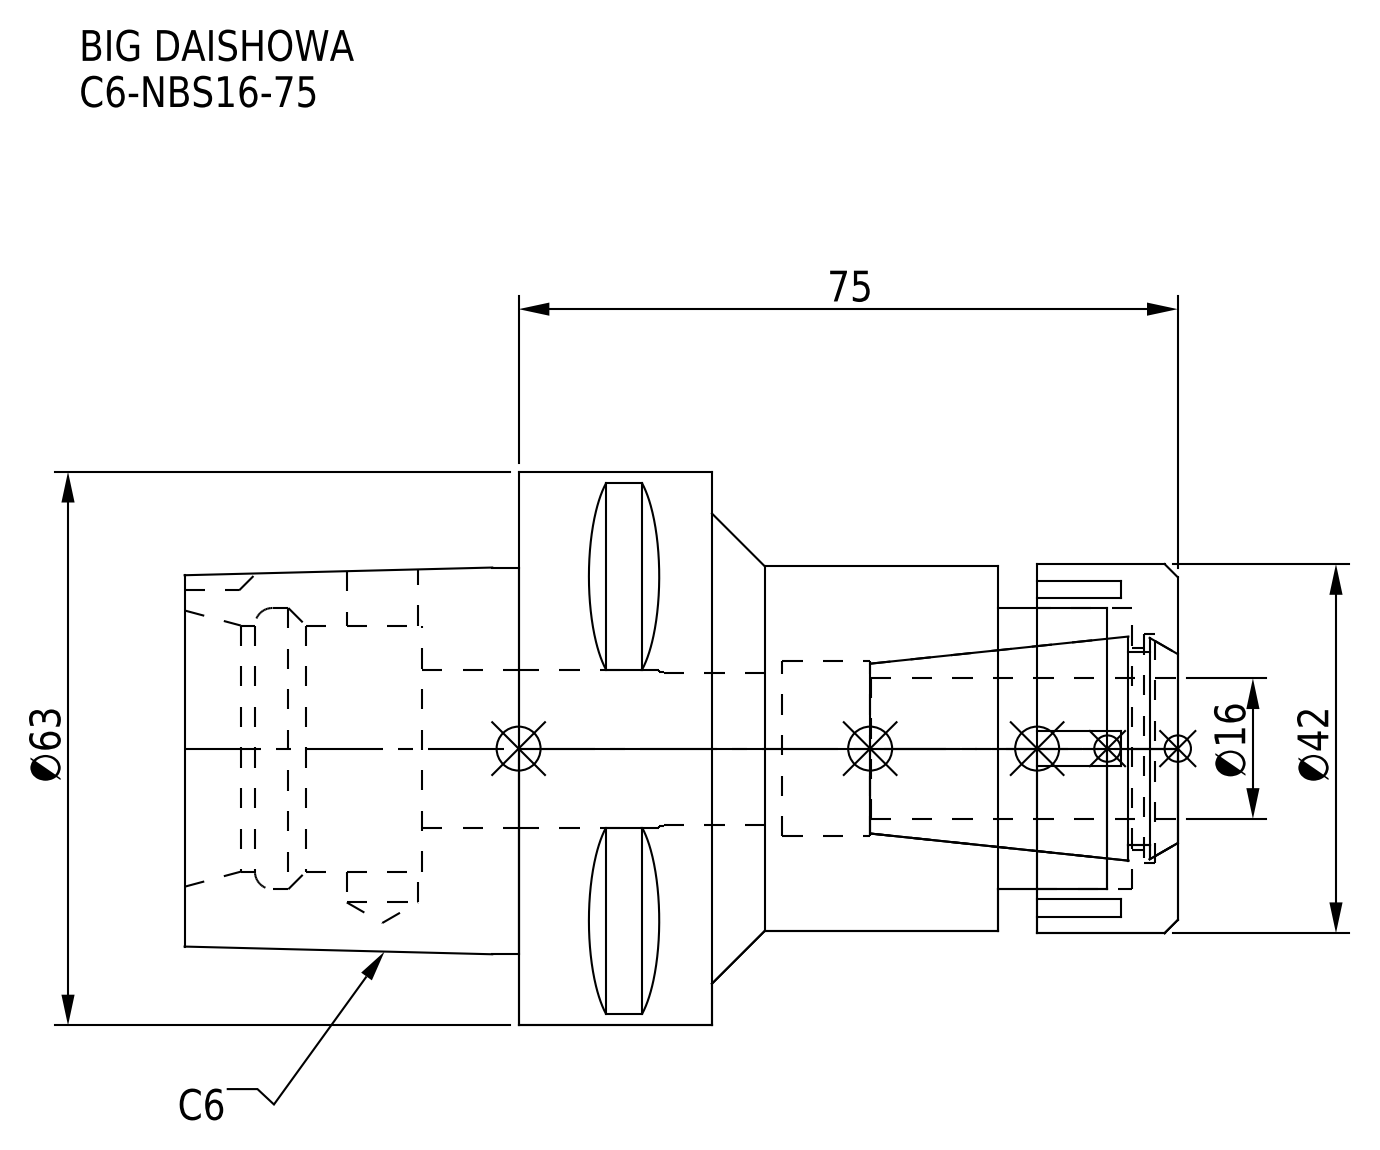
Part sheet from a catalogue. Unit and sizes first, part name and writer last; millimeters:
Units: millimetres
Overall size (bounding box): 113 × 63 × 63
Round holes (diameter × count): ⌀8.1 ×1, ⌀17.3 ×1, ⌀17.5 ×1, ⌀18 ×1, ⌀20 ×1, ⌀23 ×1, ⌀26 ×1, ⌀28 ×1, ⌀32 ×1
Round bosses / shafts (diameter × count): ⌀63 ×1, ⌀42 ×1, ⌀41.5 ×1
Partial cylindrical surfaces — rounded edges, fillets, slot ends (radius × count): R5 ×1
Main face-to-face distances: 22, 53, 75, 37, 8, 54.5, 20.5, 32.5, 16, 59
Volume: 146 721 mm³ · Surface area: 33 815 mm²
Bodies: 2 solids, 112 faces (61 planar, 33 cylindrical, 18 other)
Part name (STEP PRODUCT): NBN16_1.stp; C6-NBS16-75.stp; C6-NBS16-75-FreeParts; C6-NBS16-75 (+3 more)
STEP written by: SolidWorks 2019 (CONFIG_CONTROL_DESIGN)
